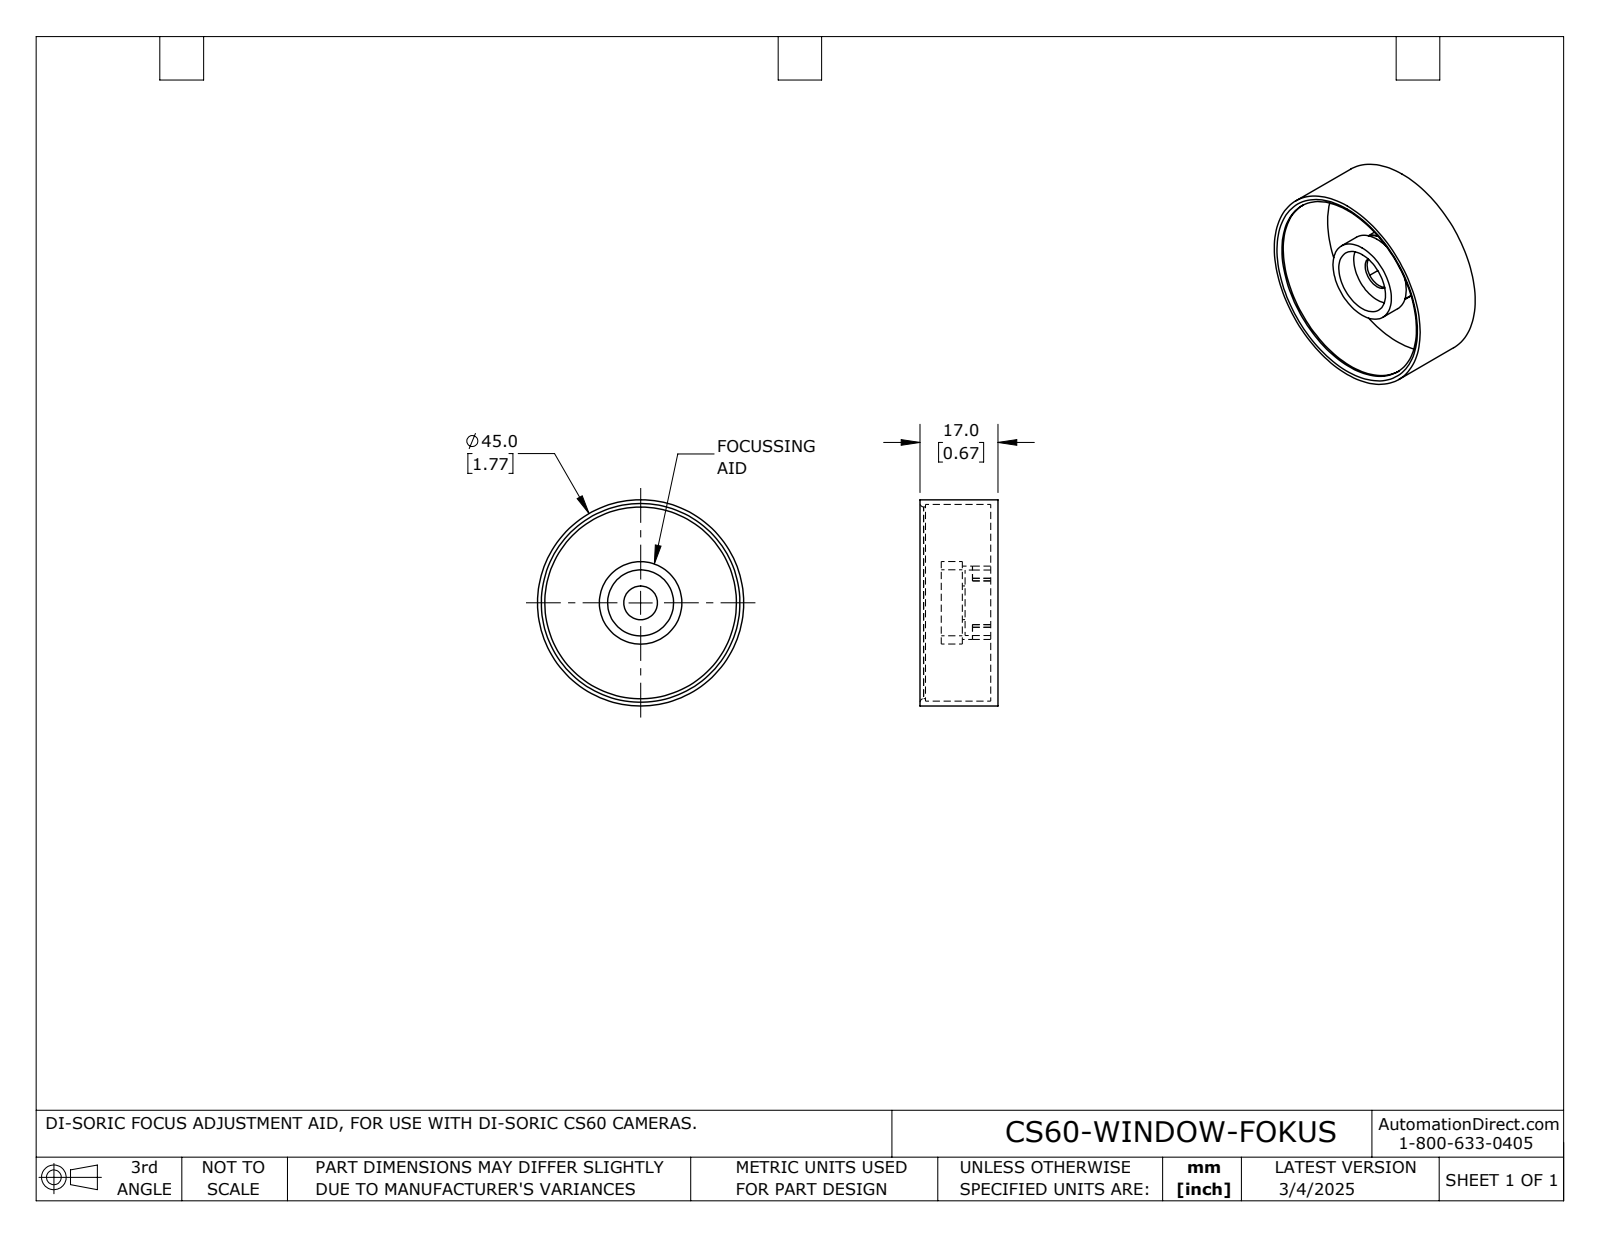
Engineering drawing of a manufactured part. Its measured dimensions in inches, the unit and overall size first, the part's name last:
Units: inches
Overall size (bounding box): 1.772 × 1.772 × 0.669
Round holes (diameter × count): ⌀0.289 ×1, ⌀0.562 ×1, ⌀0.567 ×1, ⌀1.647 ×1, ⌀1.69 ×1
Round bosses / shafts (diameter × count): ⌀1.772 ×1, ⌀0.709 ×1, ⌀0.63 ×1
Partial cylindrical surfaces — rounded edges, fillets, slot ends (radius × count): R0.281 ×1
Main face-to-face distances: 0.063, 0.307, 0.244, 0.283, 0.22, 0.024, 0.669, 0.607, 0.386, 0.363
Volume: 0.339 in³ · Surface area: 14.35 in²
Bodies: 2 solids, 35 faces (22 planar, 12 cylindrical, 1 other)
Part name (STEP PRODUCT): CS60-WINDOW-FOKUS
STEP written by: SolidWorks 2024 (AUTOMOTIVE_DESIGN)
